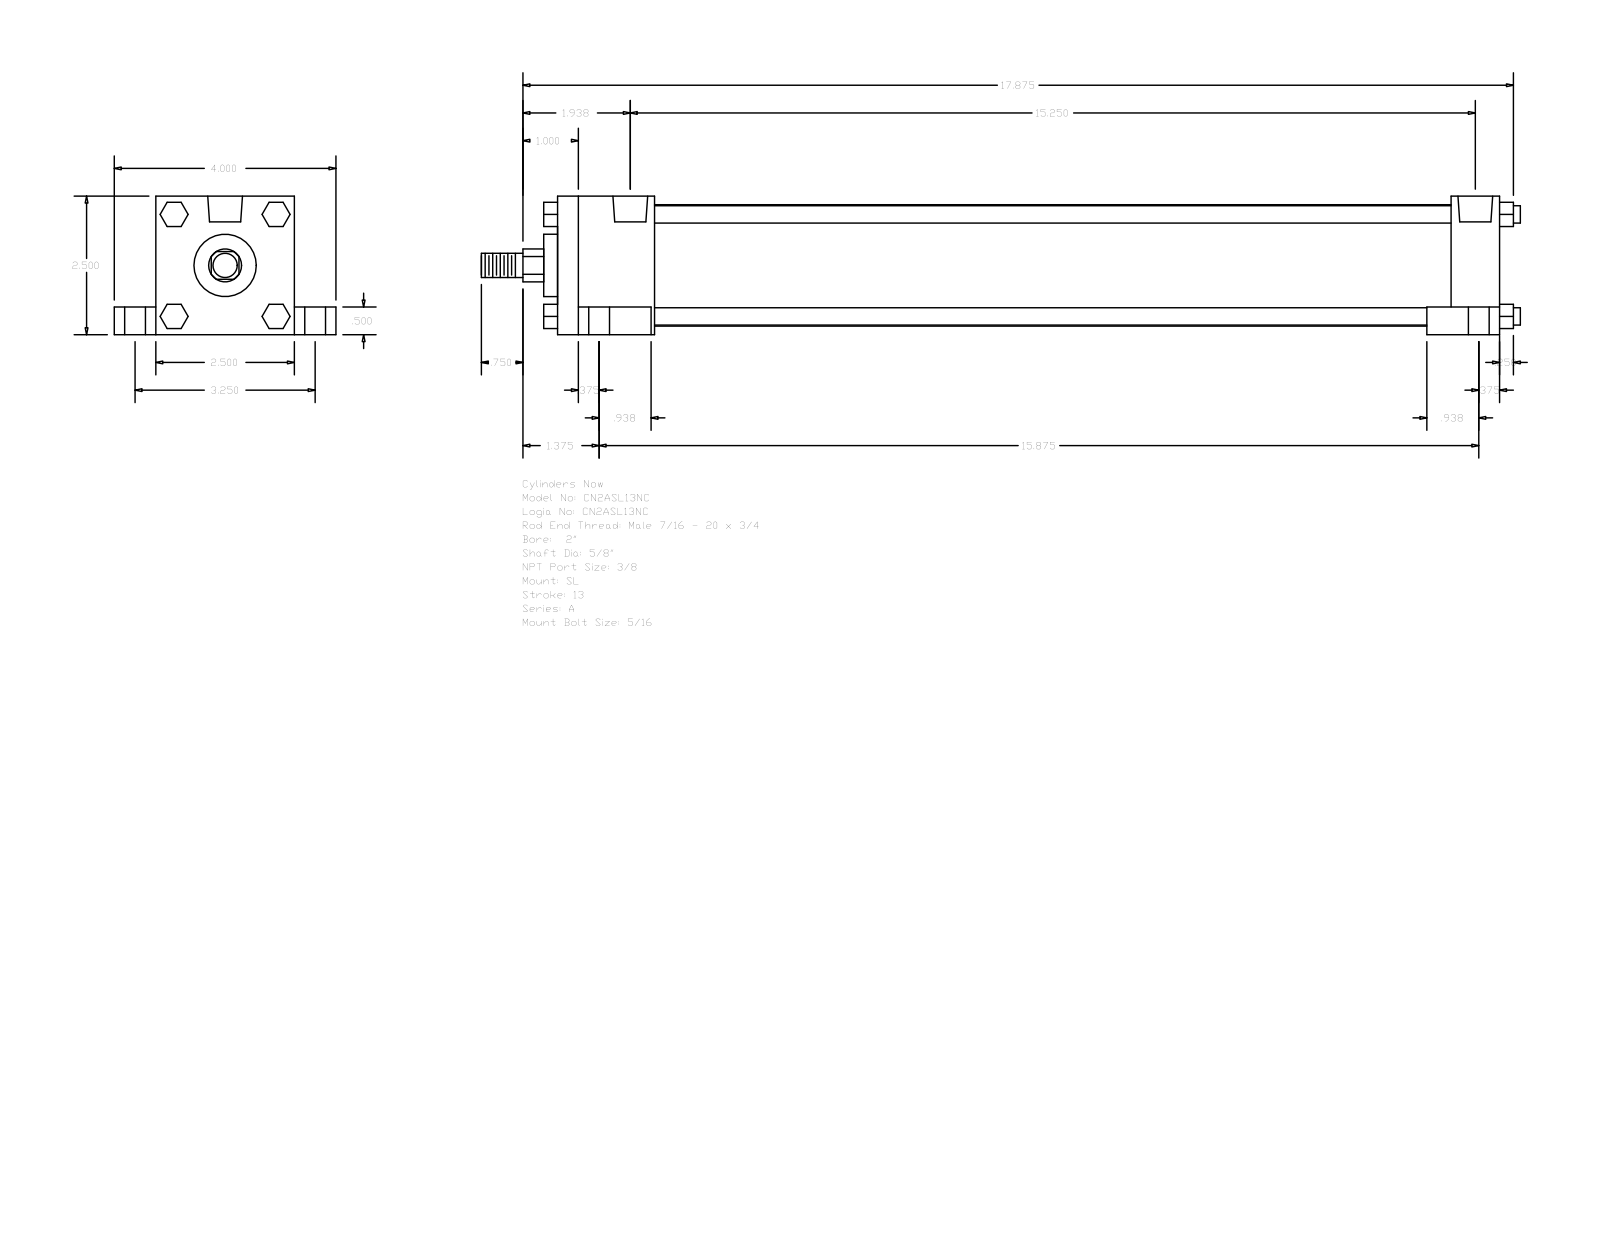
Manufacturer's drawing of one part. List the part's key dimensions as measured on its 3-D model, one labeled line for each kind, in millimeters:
Part name (STEP PRODUCT): A_SL__0200_0.625
STEP written by: GSSL Pune (CONFIG_CONTROL_DESIGN)
Units: millimetres
Bodies: 0 solids, 148 faces (112 planar, 36 cylindrical, 0 other)
Overall size (bounding box): 476.25 × 101.6 × 63.5
Round holes (diameter × count): ⌀5.56 ×4, ⌀9.53 ×4, ⌀15.88 ×4, ⌀15.93 ×2
Round bosses / shafts (diameter × count): ⌀7.94 ×4, ⌀55.63 ×1, ⌀28.57 ×1, ⌀15.88 ×1, ⌀11.11 ×1
Partial cylindrical surfaces — rounded edges, fillets, slot ends (radius × count): R7.54 ×1
Main face-to-face distances: 63.5, 431.8, 50.8, 12.7, 19.05, 82.55, 44.45, 387.35, 409.57, 365.12
Hole centre spacings: 41.3, 41.64, 43.67, 45.13, 82.54, 379.4, 387.17, 391.12
